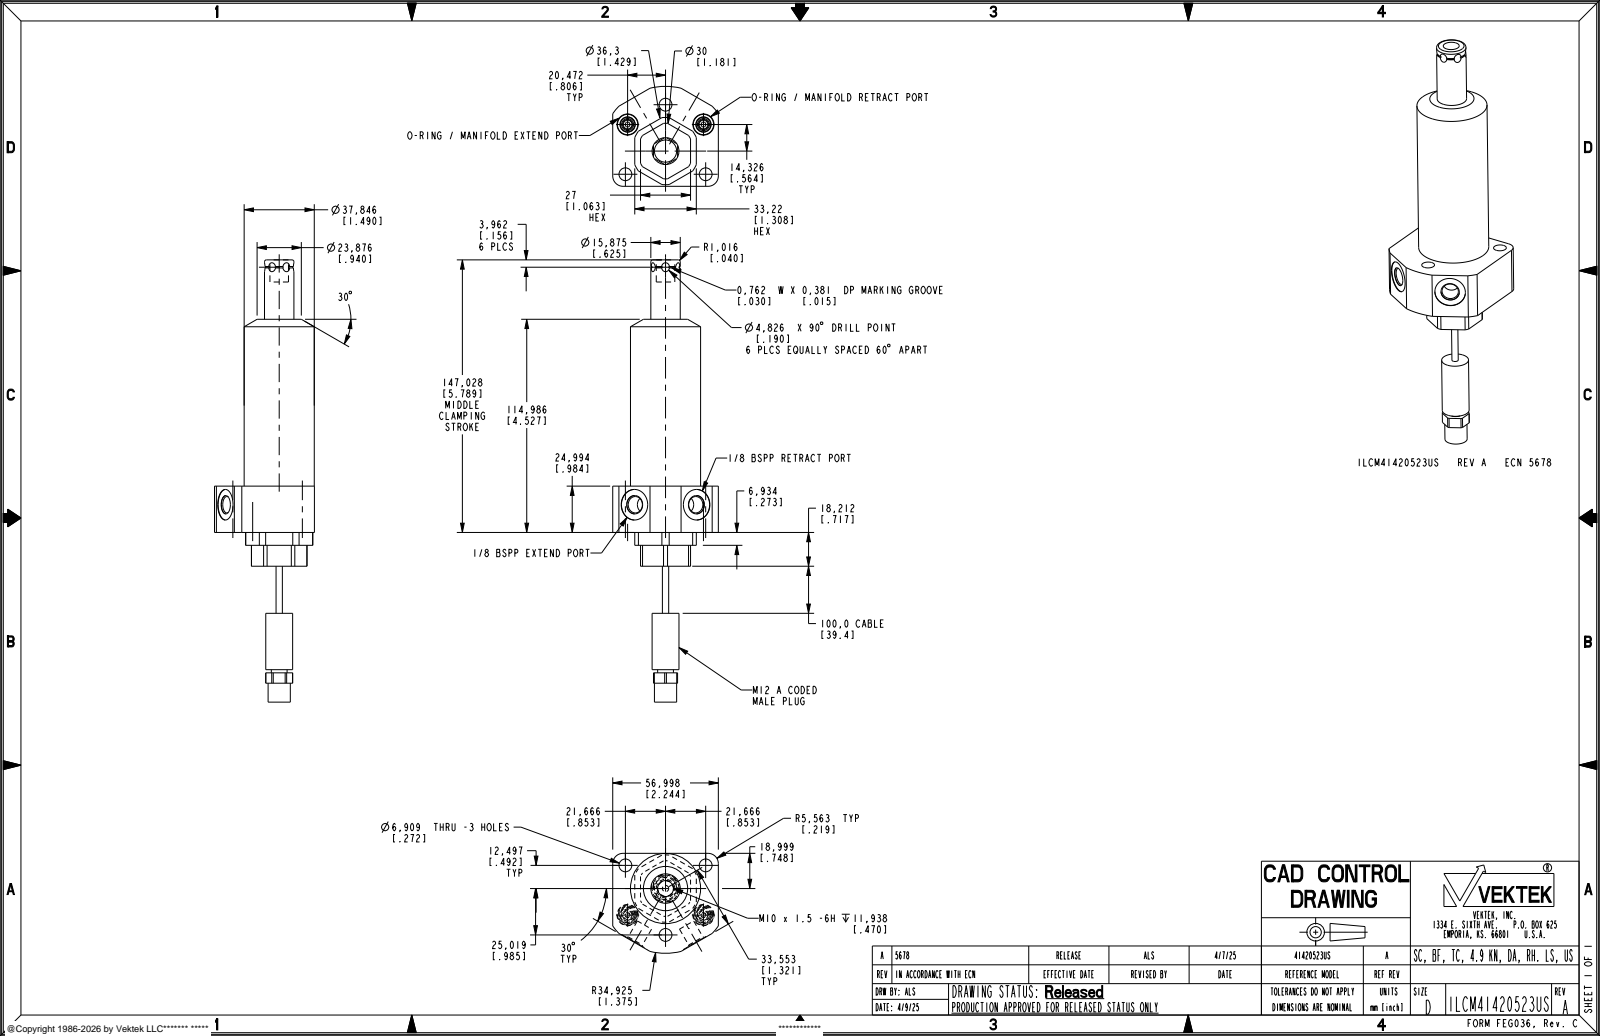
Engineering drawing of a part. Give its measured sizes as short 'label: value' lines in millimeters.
name: ILCM41420523US
written by: CREO PARAMETRIC BY PTC INC, 2021164 (AUTOMOTIVE_DESIGN)
unit: mm
bodies: 1 solid, 194 faces (79 planar, 81 cylindrical, 34 other)
size: 238.54 × 69.92 × 65
volume: 190 770 mm³; area: 30 668 mm²
holes: 3× ⌀6.91, 2× ⌀2.49, 2× ⌀6.5, 2× ⌀8.84, 2× ⌀9.91, 2× ⌀11.4, 2× ⌀16.5, 1× ⌀8.61
bosses: 2× ⌀5.49, 1× ⌀37.85, 1× ⌀15.88, 1× ⌀14.5, 1× ⌀11.99, 1× ⌀10.01, 1× ⌀8.51, 1× ⌀3.4
rounds: 2× R5.56, 1× R7.56, 1× R15, 1× R18.15, 1× R34.92
face distances: 24.99, 57, 18.22, 43.21, 3.11, 30.11, 27, 11.28, 6.94, 31.93
hole spacings: 25.02, 23.09, 24.99, 26.86, 43.33, 49.96, 40.94, 43.34
